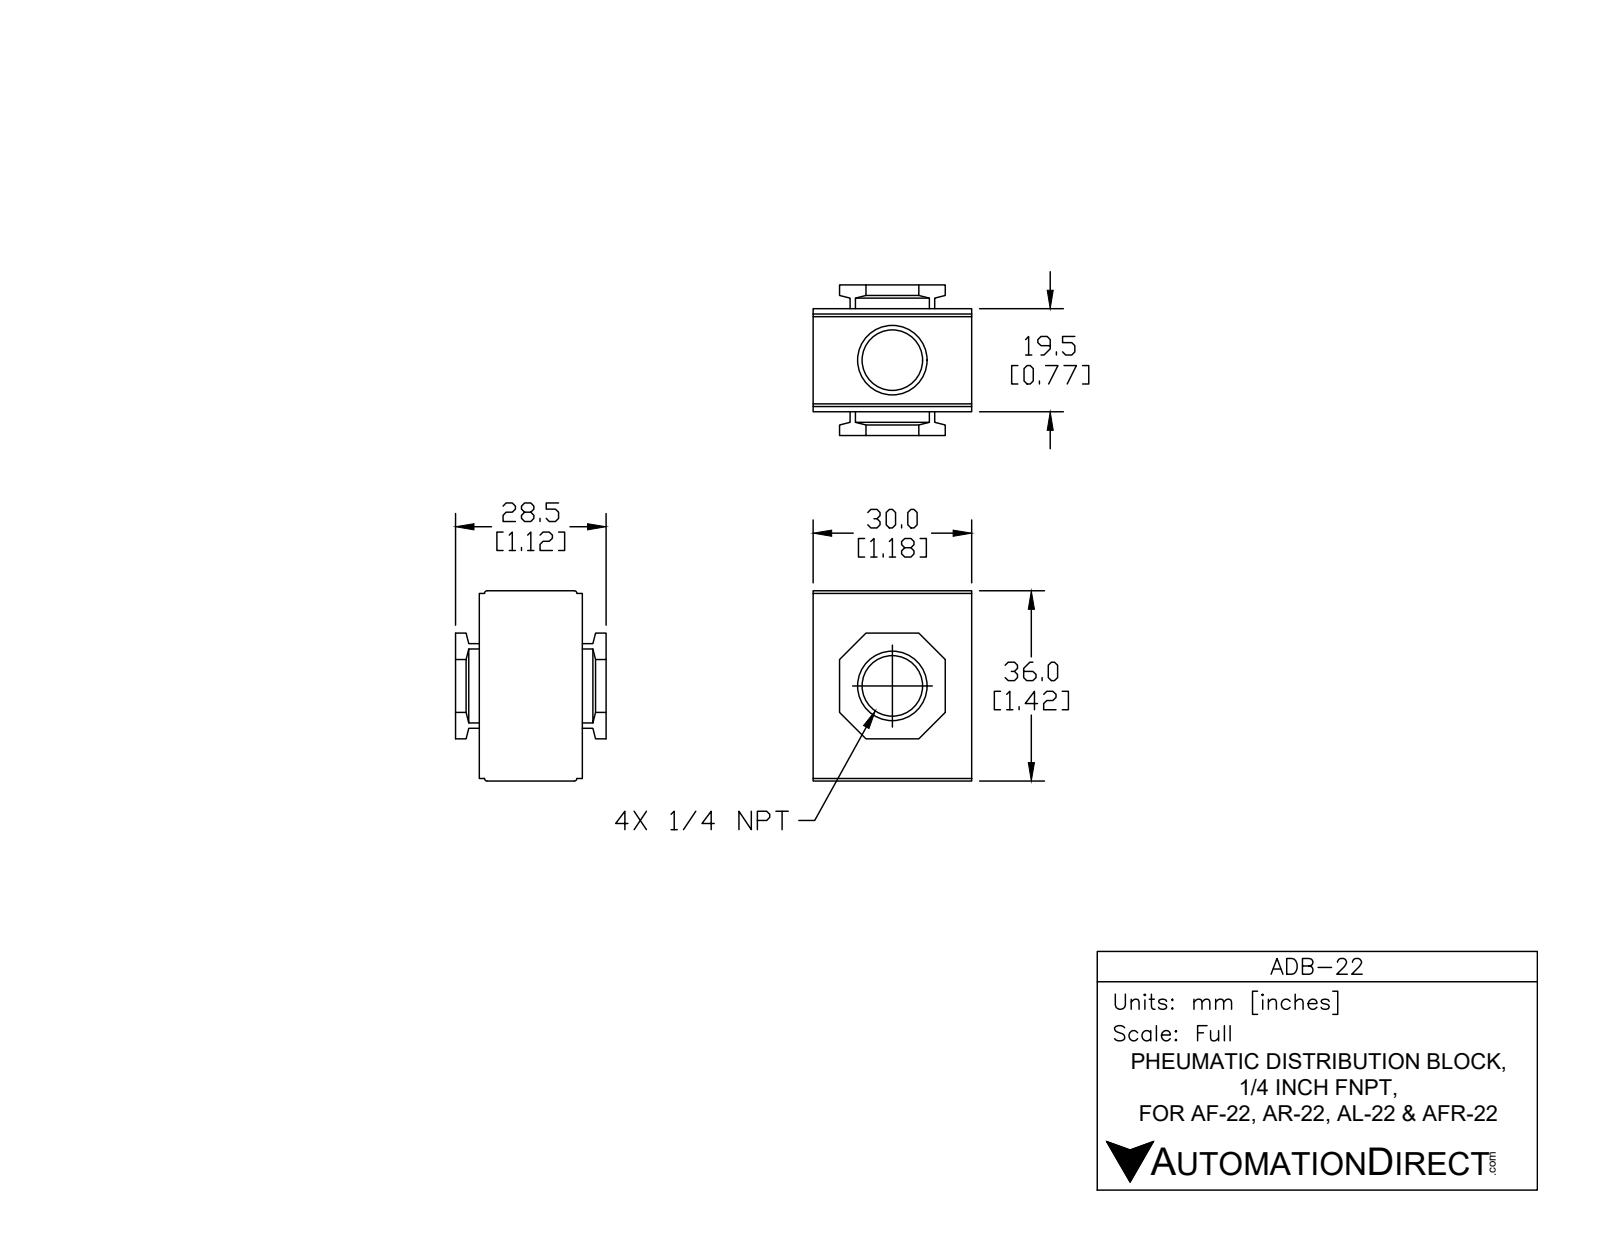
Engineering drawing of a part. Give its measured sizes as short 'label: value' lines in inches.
name: ADB-22
written by: SolidWorks 2014 (AUTOMOTIVE_DESIGN)
unit: in
bodies: 1 solid, 64 faces (44 planar, 12 cylindrical, 8 other)
size: 1.417 × 1.181 × 1.122
volume: 1.1 in³; area: 10.77 in²
holes: 2× ⌀0.451
rounds: 4× R0.02
face distances: 0.768, 1.181, 0.177, 0.945, 1.417, 1.122, 0.079, 0.709, 0.02, 1.398
